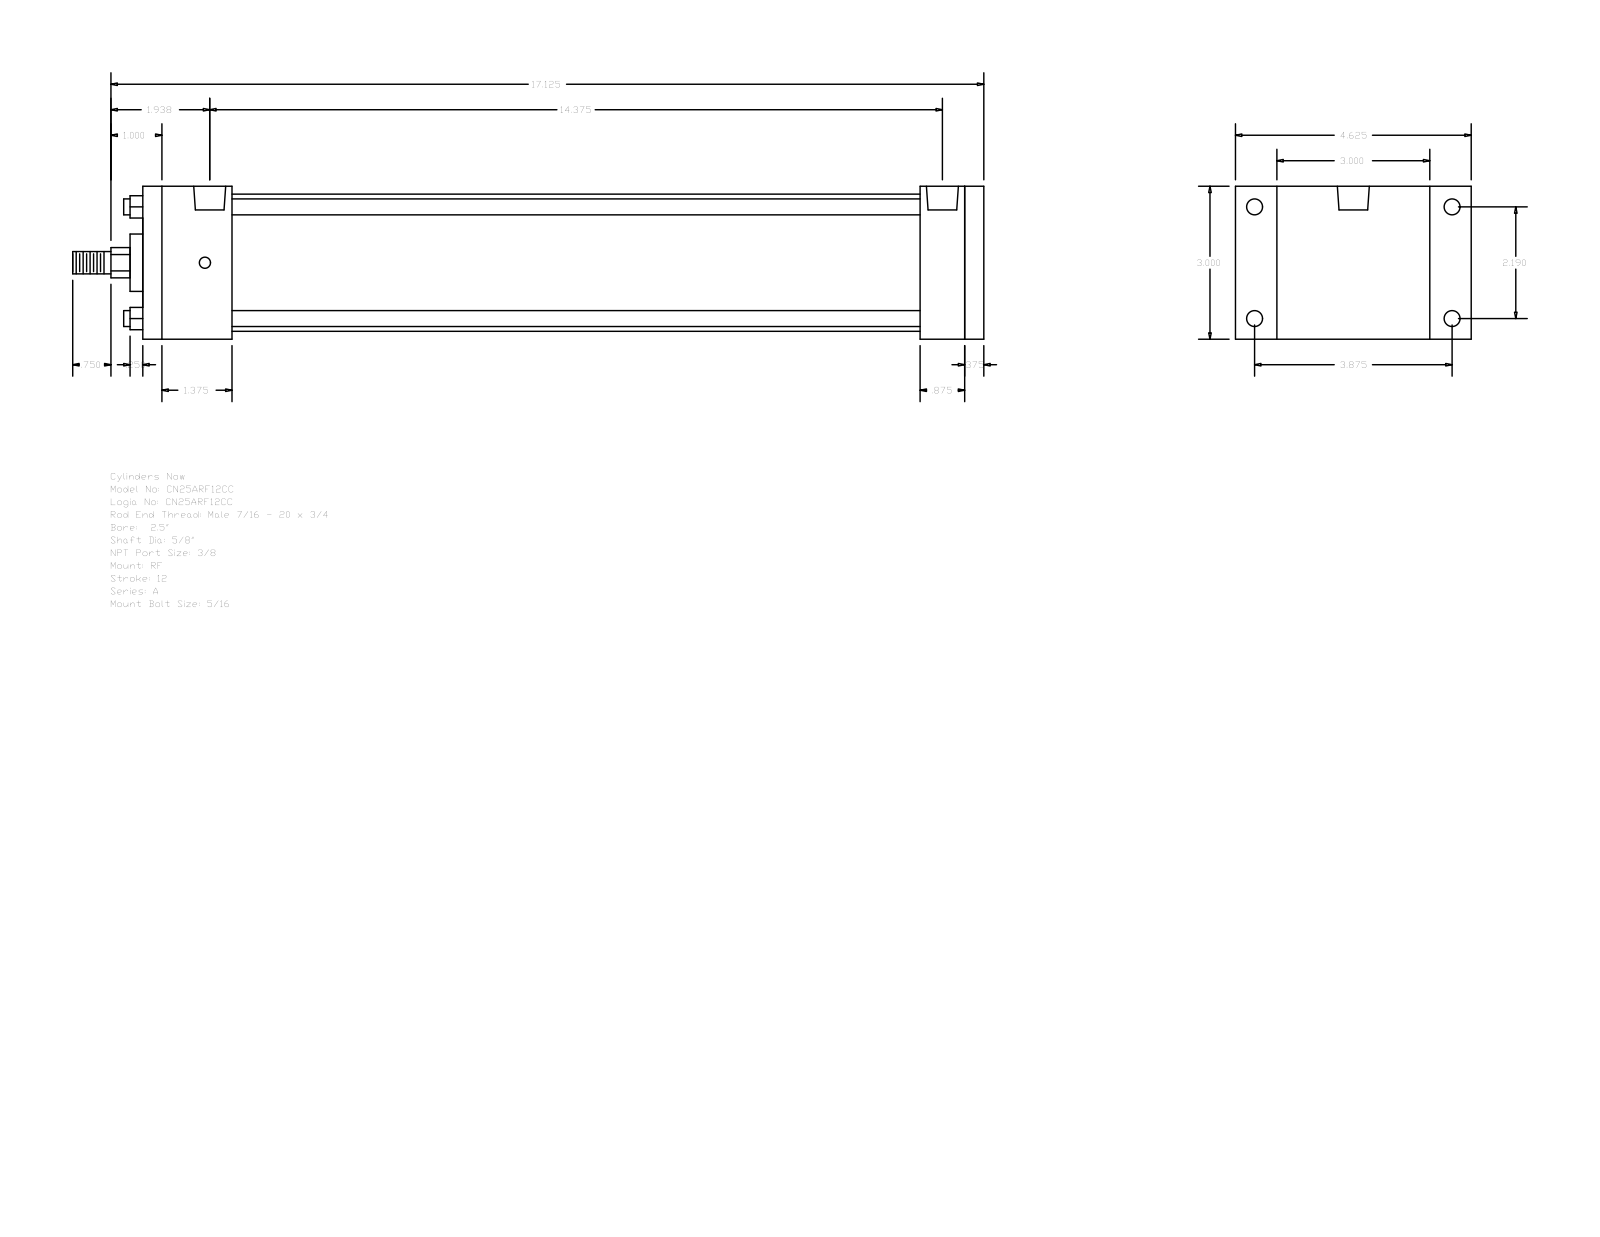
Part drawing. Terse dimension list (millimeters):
name: A_RF__0250_0.625
written by: GSSL Pune (CONFIG_CONTROL_DESIGN)
unit: mm
bodies: 0 solids, 92 faces (64 planar, 28 cylindrical, 0 other)
size: 454.02 × 117.47 × 76.2
holes: 4× ⌀5.56, 4× ⌀7.94, 2× ⌀15.93
bosses: 4× ⌀7.94, 1× ⌀68.33, 1× ⌀28.57, 1× ⌀15.88, 1× ⌀11.11
rounds: 1× R7.54
face distances: 76.2, 419.1, 9.53, 409.57, 44.45, 31.75, 387.35, 342.9, 365.12, 374.65
hole spacings: 2.38, 55.62, 98.42, 113.05, 367.51, 369.89, 365.13
